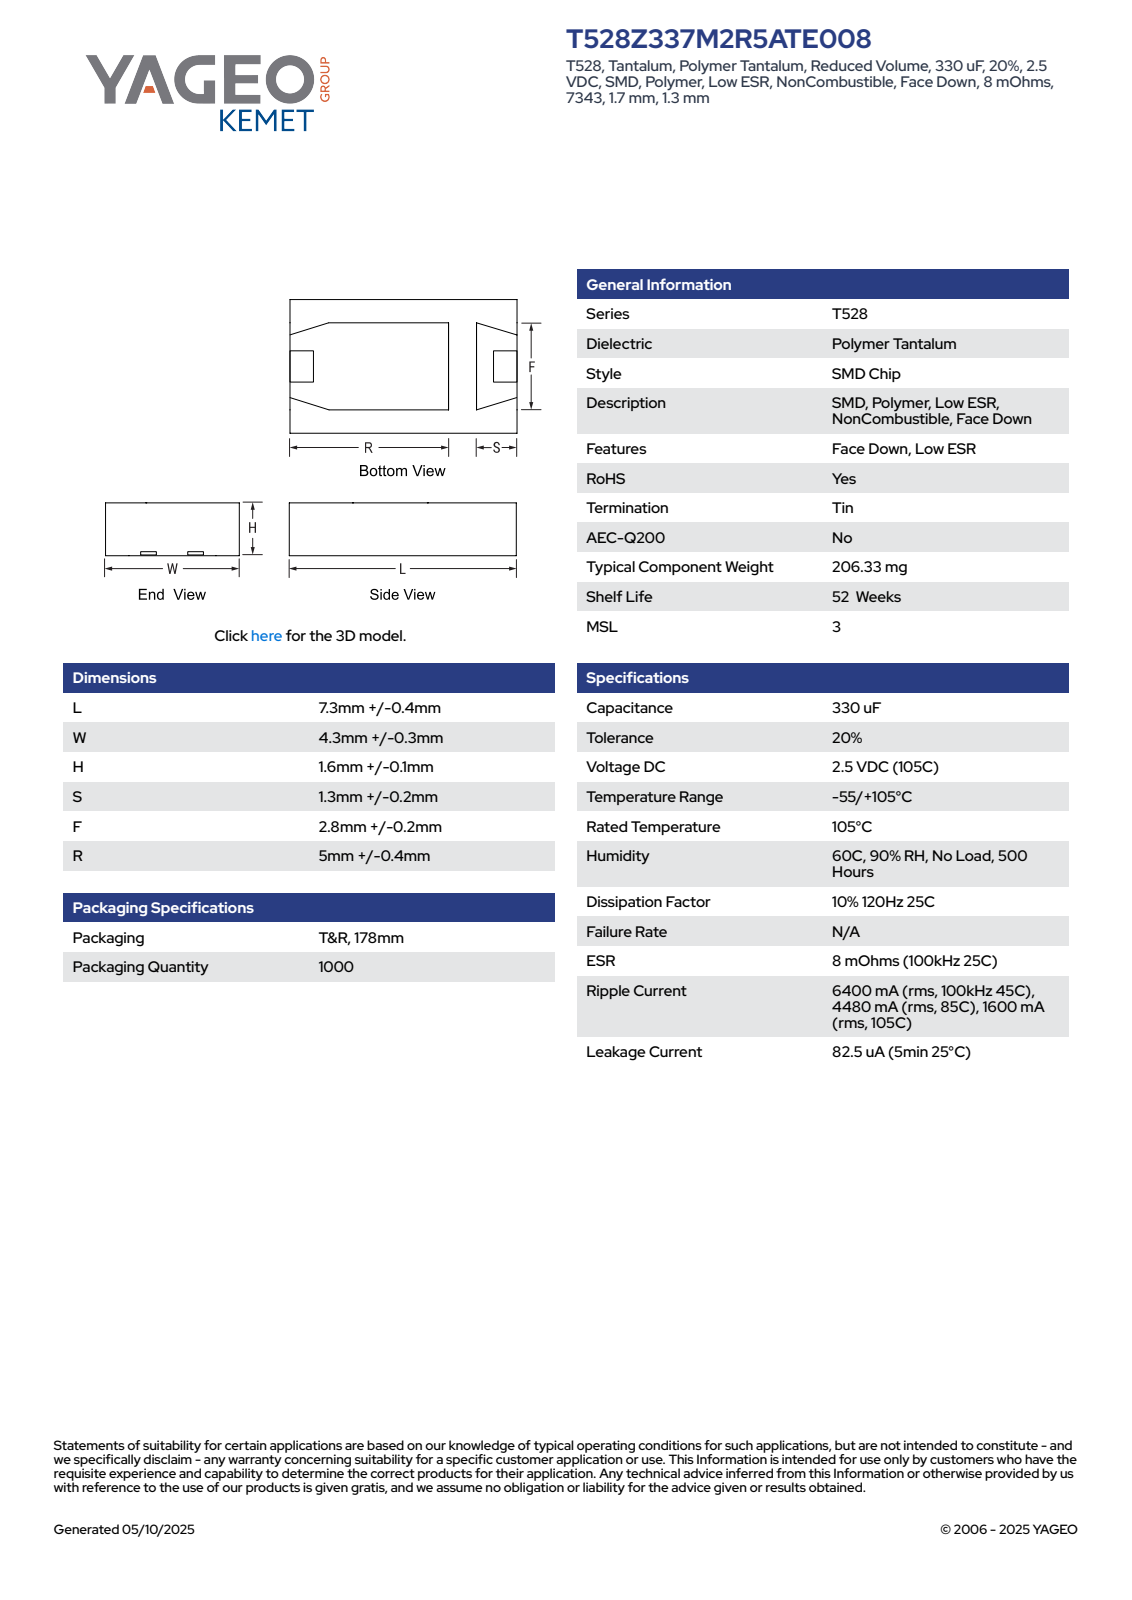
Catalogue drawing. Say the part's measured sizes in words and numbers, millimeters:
The part is named "CTS_TWZ_7343_L7.7W4.6H1.7S1.5F3R5.4". Its 3-D file was written by "SolidWorks 2014 (AUTOMOTIVE_DESIGN)". It is 4 solids with 100 faces: 100 planar, 0 cylindrical and 0 other. Overall it measures 7.71 by 4.6 by 1.71 millimeters. Its volume is 60 cubic millimeters and its surface area 119 square millimeters. The main face-to-face distances are 1.71, 1.7, 4.6, 7.7, 7.71, 7.72, 0.8, 3.8, 1.4, 1.8.
